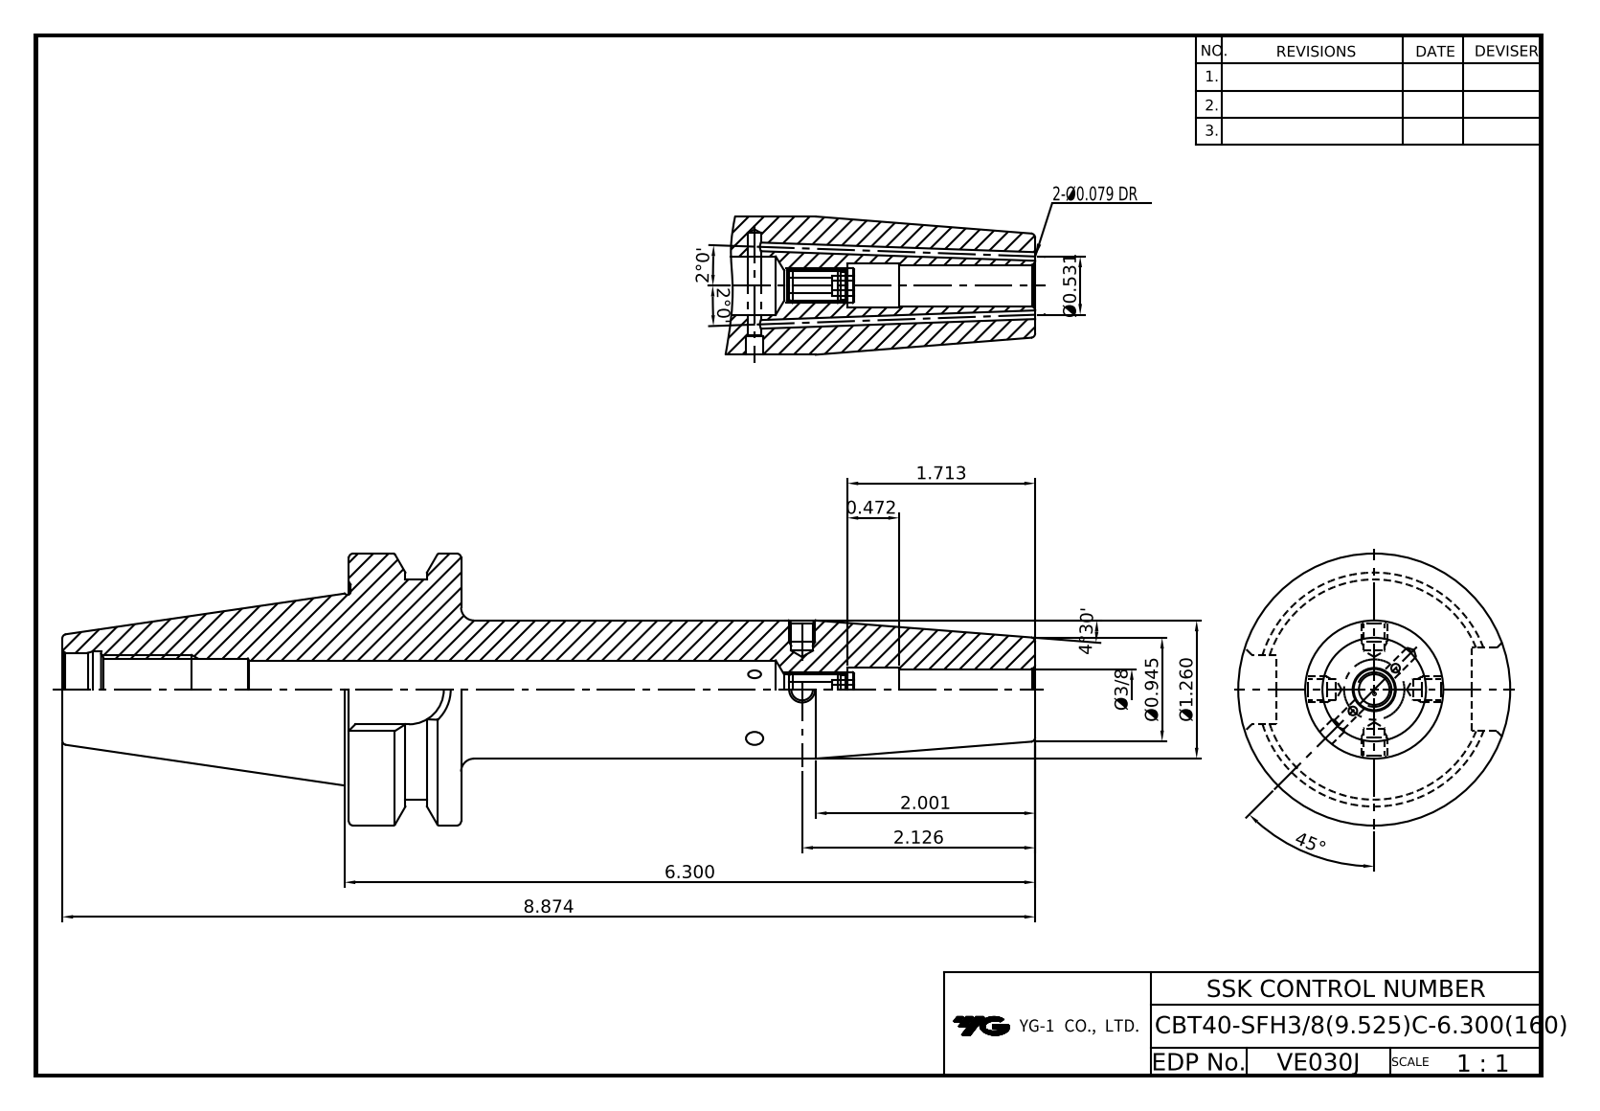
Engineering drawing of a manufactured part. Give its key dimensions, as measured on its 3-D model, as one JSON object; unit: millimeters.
{"part_name": "CBT40-SFH9_525C-160", "step_written_by": "CREO PARAMETRIC BY PTC INC, 2018500 (CONFIG_CONTROL_DESIGN)", "units": "millimeters", "bodies": {"solids": 1, "faces": 92, "planar": 22, "cylindrical": 28, "other": 42}, "overall_size": [225.4, 63, 63], "volume_mm3": 202320, "surface_area_mm2": 40953, "round_holes": [[8, 1], [9.53, 1], [10.13, 1], [13.5, 1], [14, 1], [16, 1], [17, 1], [17.6, 1]], "round_bosses_or_shafts": [[63, 1], [51, 1], [44, 1], [32, 1]], "partial_cylinders_radius": [[8.05, 1]], "face_to_face_distances": [25, 45.2, 158, 133, 17.1, 7.9, 140.9, 12.1, 5, 12.9]}
